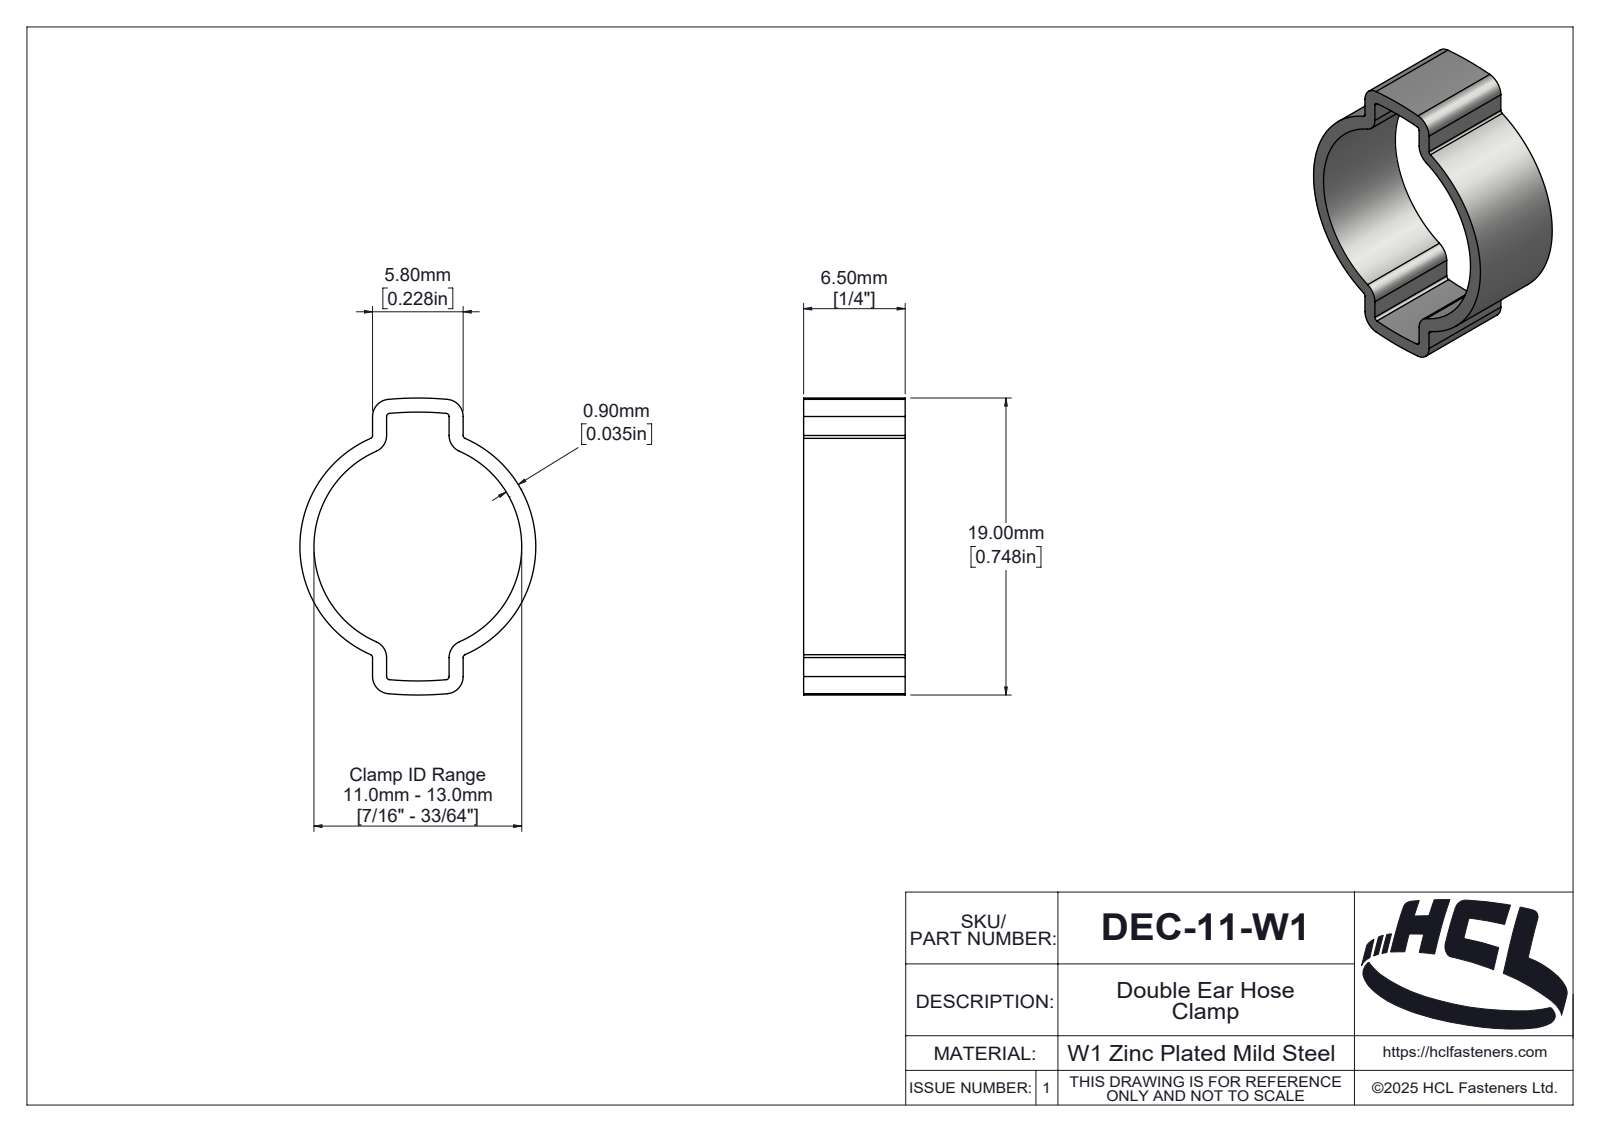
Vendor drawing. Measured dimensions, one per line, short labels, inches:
name: DEC-11-W1
written by: SolidWorks 2025 (AUTOMOTIVE_DESIGN)
unit: in
bodies: 1 solid, 137 faces (12 planar, 76 cylindrical, 49 other)
size: 0.748 × 0.594 × 0.256
volume: 0.019 in³; area: 1.2 in²
rounds: 8× R0.008, 8× R0.043, 2× R0.789, 2× R0.825, 1× R0.005, 1× R0.021, 1× R0.026, 1× R0.028
face distances: 0.256, 0.035, 0.193, 0.228, 0.157, 0.107, 0.072, 0.086, 0.121, 0.111
